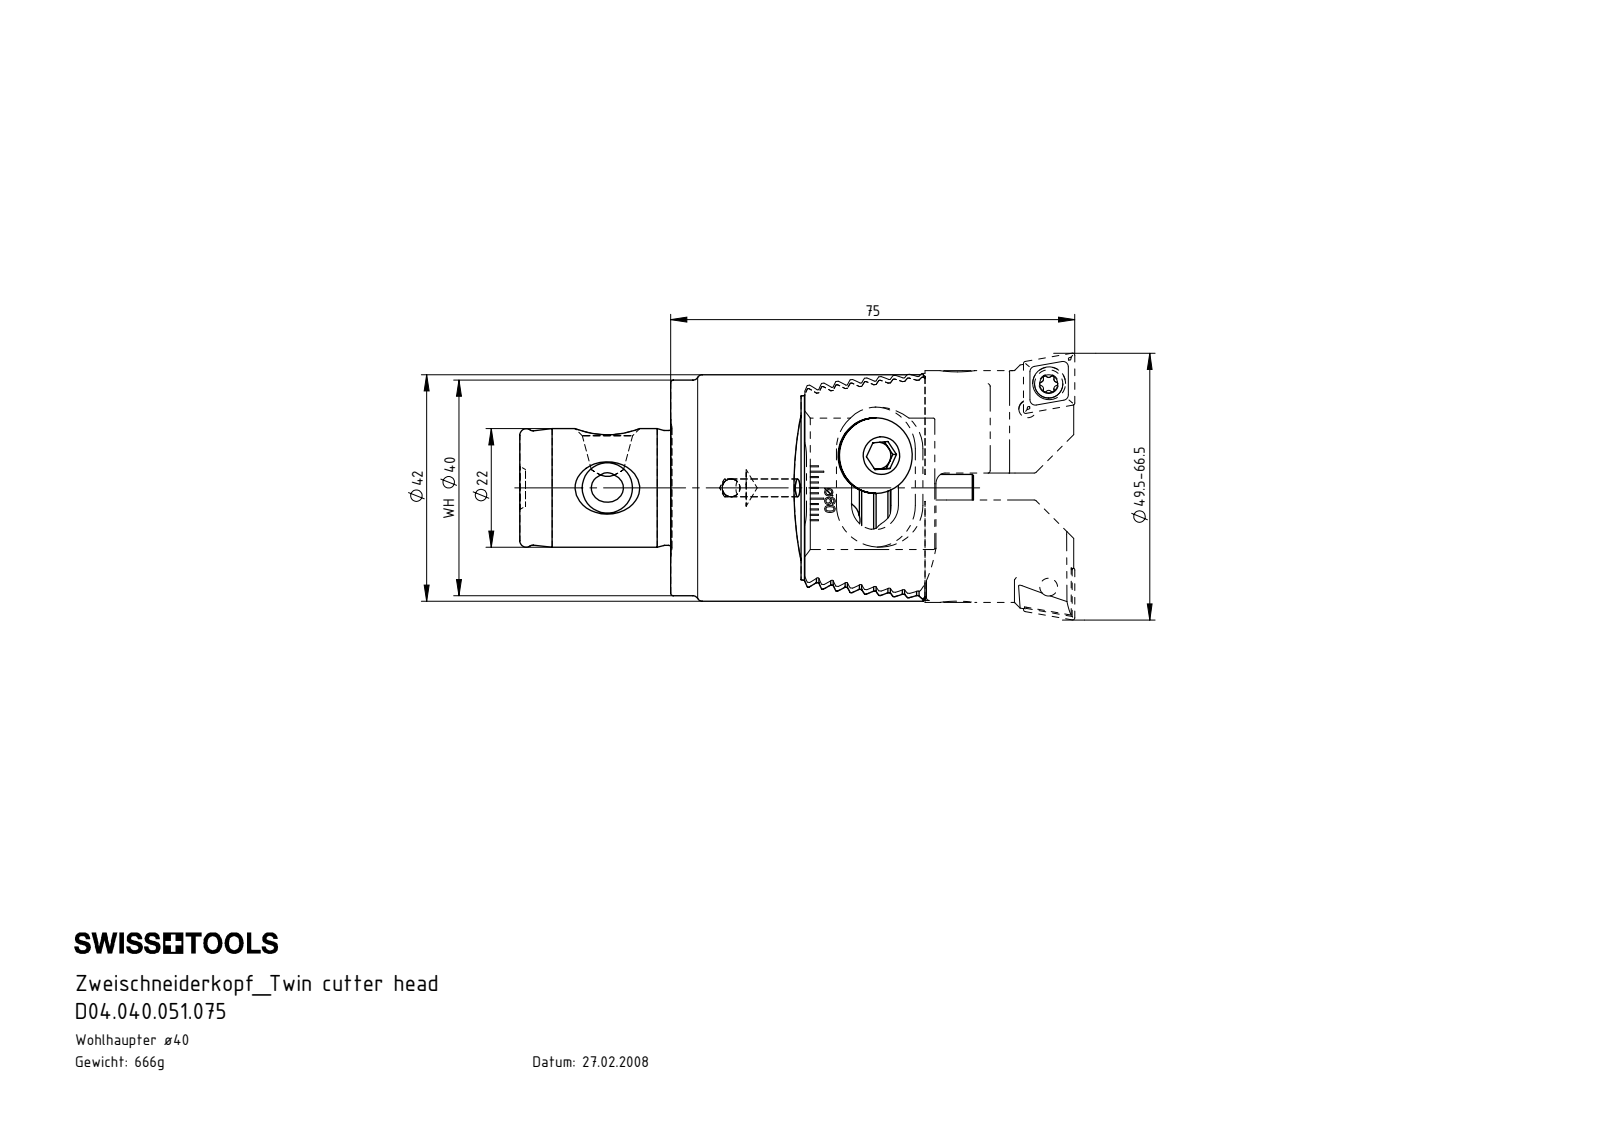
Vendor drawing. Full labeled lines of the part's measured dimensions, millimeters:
Part name (STEP PRODUCT): Z42-ER1.002.020_A; Z42-ER1.003.020_A_gespannt; Z42-ER1.001.020; Z42-ER2.001.019_A (+7 more)
STEP written by: SolidWorks 2015 (AUTOMOTIVE_DESIGN)
Units: millimetres
Bodies: 14 solids, 969 faces (487 planar, 216 cylindrical, 266 other)
Overall size (bounding box): 103 × 50 × 42
Volume: 84 929 mm³ · Surface area: 29 435 mm²
Round holes (diameter × count): ⌀3.3 ×8, ⌀6.8 ×3, ⌀1.6 ×2, ⌀4.4 ×2, ⌀6.1 ×2, ⌀8.4 ×2, ⌀9 ×2, ⌀5 ×1
Round bosses / shafts (diameter × count): ⌀14 ×4, ⌀4 ×4, ⌀8 ×2, ⌀5.25 ×2, ⌀42 ×1, ⌀40 ×1, ⌀22 ×1, ⌀21.3 ×1
Partial cylindrical surfaces — rounded edges, fillets, slot ends (radius × count): R0.2 ×18, R0.2 ×16, R0.34 ×12, R0.59 ×12, R2 ×4, R4.5 ×4, R7.75 ×4, R12 ×4
Main face-to-face distances: 2.38, 4.76, 2.42, 7.14, 2.34, 9.52, 4.8, 4.72, 11.9, 14.29
Hole centre spacings: 6.07, 6.19, 12, 34.15, 34.25, 38.67, 23.18, 29.28
